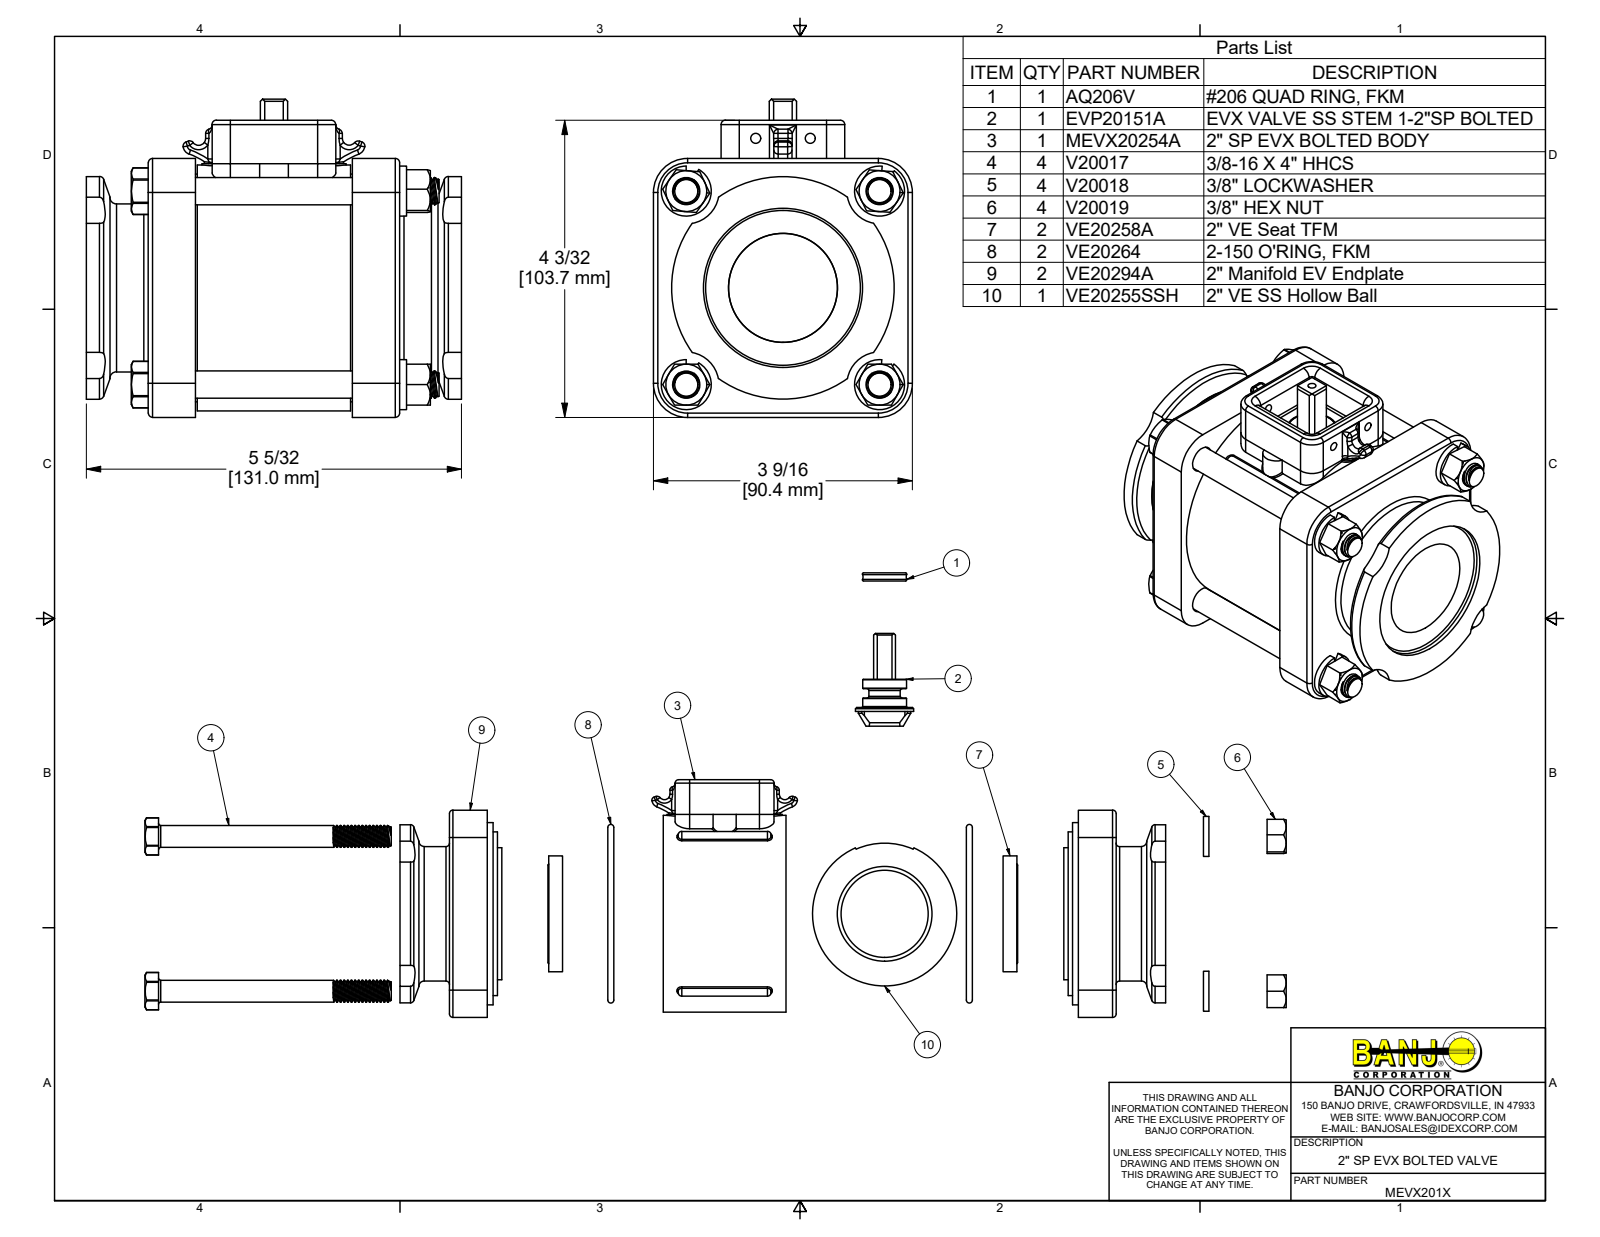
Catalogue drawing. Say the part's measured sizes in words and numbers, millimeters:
The part is named "MEVX201X; MEVX20254A; MEVX20254AX; V20017 (+8 more)". Its 3-D file was written by "Autodesk Inventor 2019 (AUTOMOTIVE_DESIGN)". It is 22 solids with 1039 faces: 202 planar, 398 cylindrical and 439 other. Overall it measures 131 by 111.1 by 90.4 millimeters. Its volume is 551 900 cubic millimeters and its surface area 159 500 square millimeters. Round holes: 4 of diameter 7.8, 4 of diameter 9.8, 4 of diameter 10.3, 2 of diameter 3.4, 2 of diameter 38.1, 1 of diameter 19.3, 1 of diameter 25.9, 1 of diameter 38, 1 of diameter 50.7, 1 of diameter 55.6, 1 of diameter 65, 1 of diameter 77.8. Round bosses or shafts: 60 of diameter 8.2, 4 of diameter 17.4, 4 of diameter 9.5, 1 of diameter 85.9, 1 of diameter 79.5, 1 of diameter 71.4, 1 of diameter 58.7, 1 of diameter 57.7. Partial cylindrical surfaces (rounded edges, fillets, slot ends): 36 of radius 1.5, 8 of radius 0.5, 8 of radius 4.1, 6 of radius 3.2, 5 of radius 11.4, 4 of radius 0.4, 4 of radius 0.8, 4 of radius 2.3. The main face-to-face distances are 16.5, 71.3, 21, 66.9, 4.4, 50.4, 87.8, 21.6, 38.1, 42.5. The hole center spacings are 47.8, 67.5, 30.5, 47, 53, 89.3, 95.5, 96.2.
